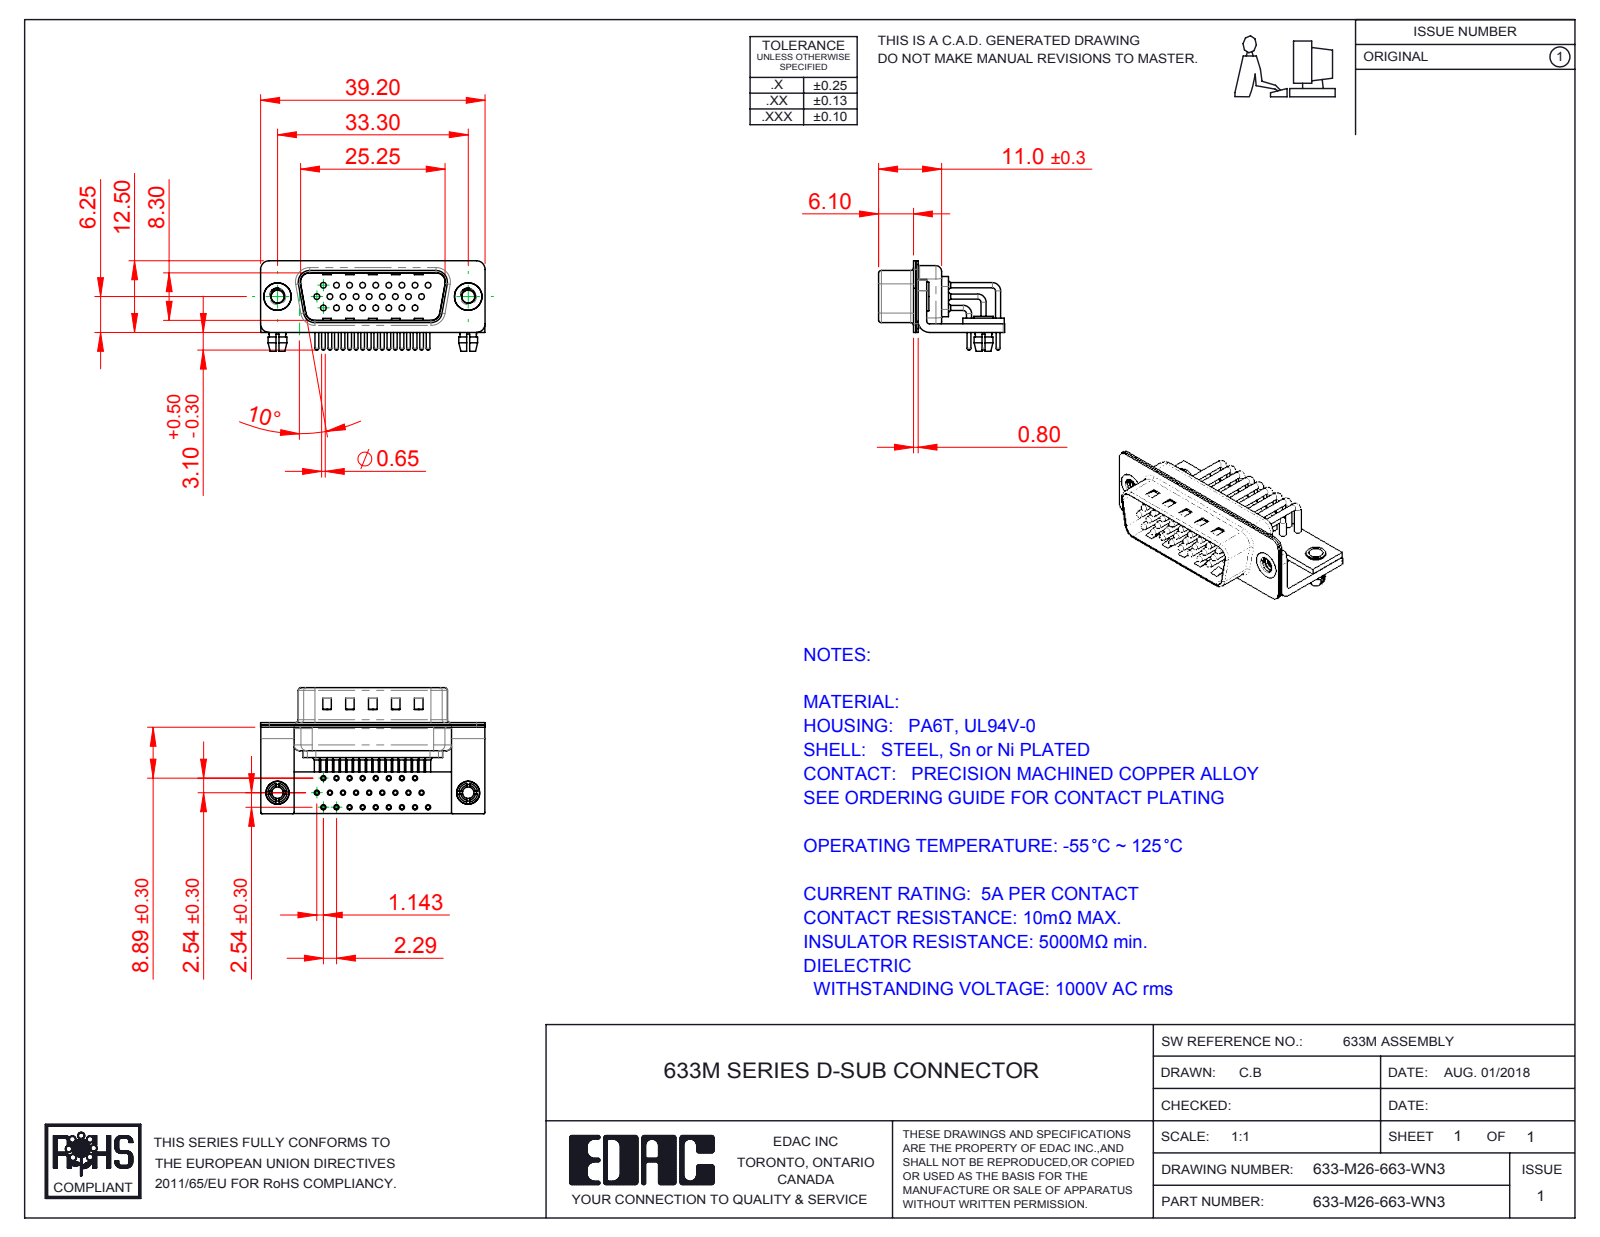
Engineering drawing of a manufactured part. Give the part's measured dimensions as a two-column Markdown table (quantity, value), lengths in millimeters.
| quantity | value |
| --- | --- |
| part name | 633M Housing_26 Contacts; 633M Contact Row 3; 633M Stabilizer Bracket; 633M Contact Row 2 (+7 more) |
| STEP written by | SolidWorks 2016 (CONFIG_CONTROL_DESIGN) |
| units | millimeters |
| bodies | 36 solids, 3394 faces (1877 planar, 1175 cylindrical, 342 other) |
| overall size | 39.2 × 22 × 15.8 |
| volume | 2 666 mm³ |
| surface area | 8 233 mm² |
| round holes (diameter × count) | 2 × 28, 0.9 × 26, 1 × 26, 1.7 × 26, 2.26 × 2, 2.5 × 2, 3.2 × 2, 4 × 2, 4.8 × 2 |
| round bosses / shafts (diameter × count) | 1.5 × 26, 0.9 × 26, 0.65 × 26, 5 × 2, 4.9 × 2, 4 × 2, 3.4 × 2, 3.3 × 2 |
| partial cylindrical surfaces (radius × count) | 1.01 × 26, 0.25 × 16, 1.5 × 16, 2 × 13, 0.5 × 9, 1.6 × 8, 0.6 × 4, 0.65 × 4 |
| main face-to-face distances | 0.4, 1.5, 0.85, 0.8, 1, 1.25, 1.9, 10.4, 9.55, 2.5 |
| hole center spacings | 4.57, 2.29, 2.28, 3.96, 6.86, 4.27, 6.05, 2.78 |
